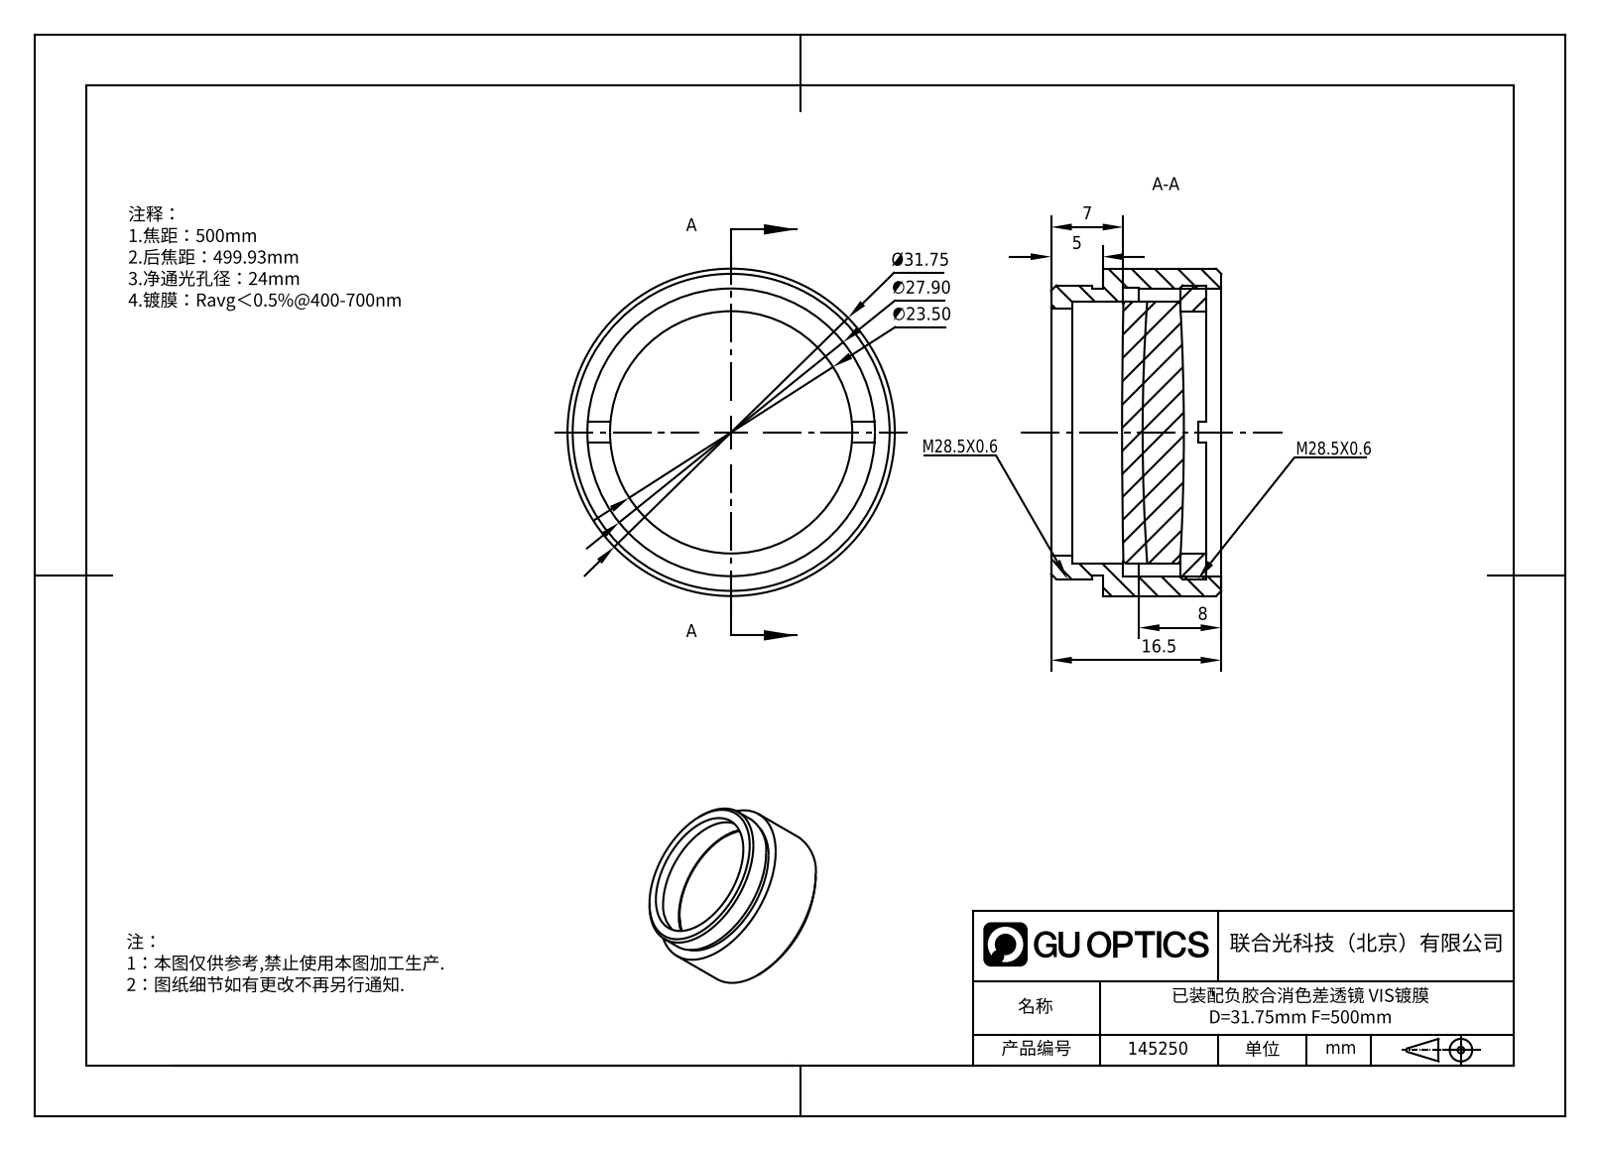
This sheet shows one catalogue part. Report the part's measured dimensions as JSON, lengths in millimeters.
{"part_name": "GL31-025B-500-VIS_Solidworks; APD-ML25-500-VIS; M28.5x0.6安装环PN35020-LM254-D1; M28.5x0.6ѹȦ", "step_written_by": "SolidWorks 2022 (AUTOMOTIVE_DESIGN)", "units": "millimeters", "bodies": {"solids": 4, "faces": 56, "planar": 16, "cylindrical": 22, "other": 18}, "overall_size": [31.76, 31.76, 16.5], "volume_mm3": 6426, "surface_area_mm2": 6935, "round_holes": [[23.5, 1], [24, 1], [27.9, 1], [28, 1]], "round_bosses_or_shafts": [[31.76, 1], [28.5, 1], [27.8, 1], [25.4, 1]], "face_to_face_distances": [2, 5, 2.5, 7.64, 10.14, 12.64, 15.14, 16.5, 11.5, 3.86]}
